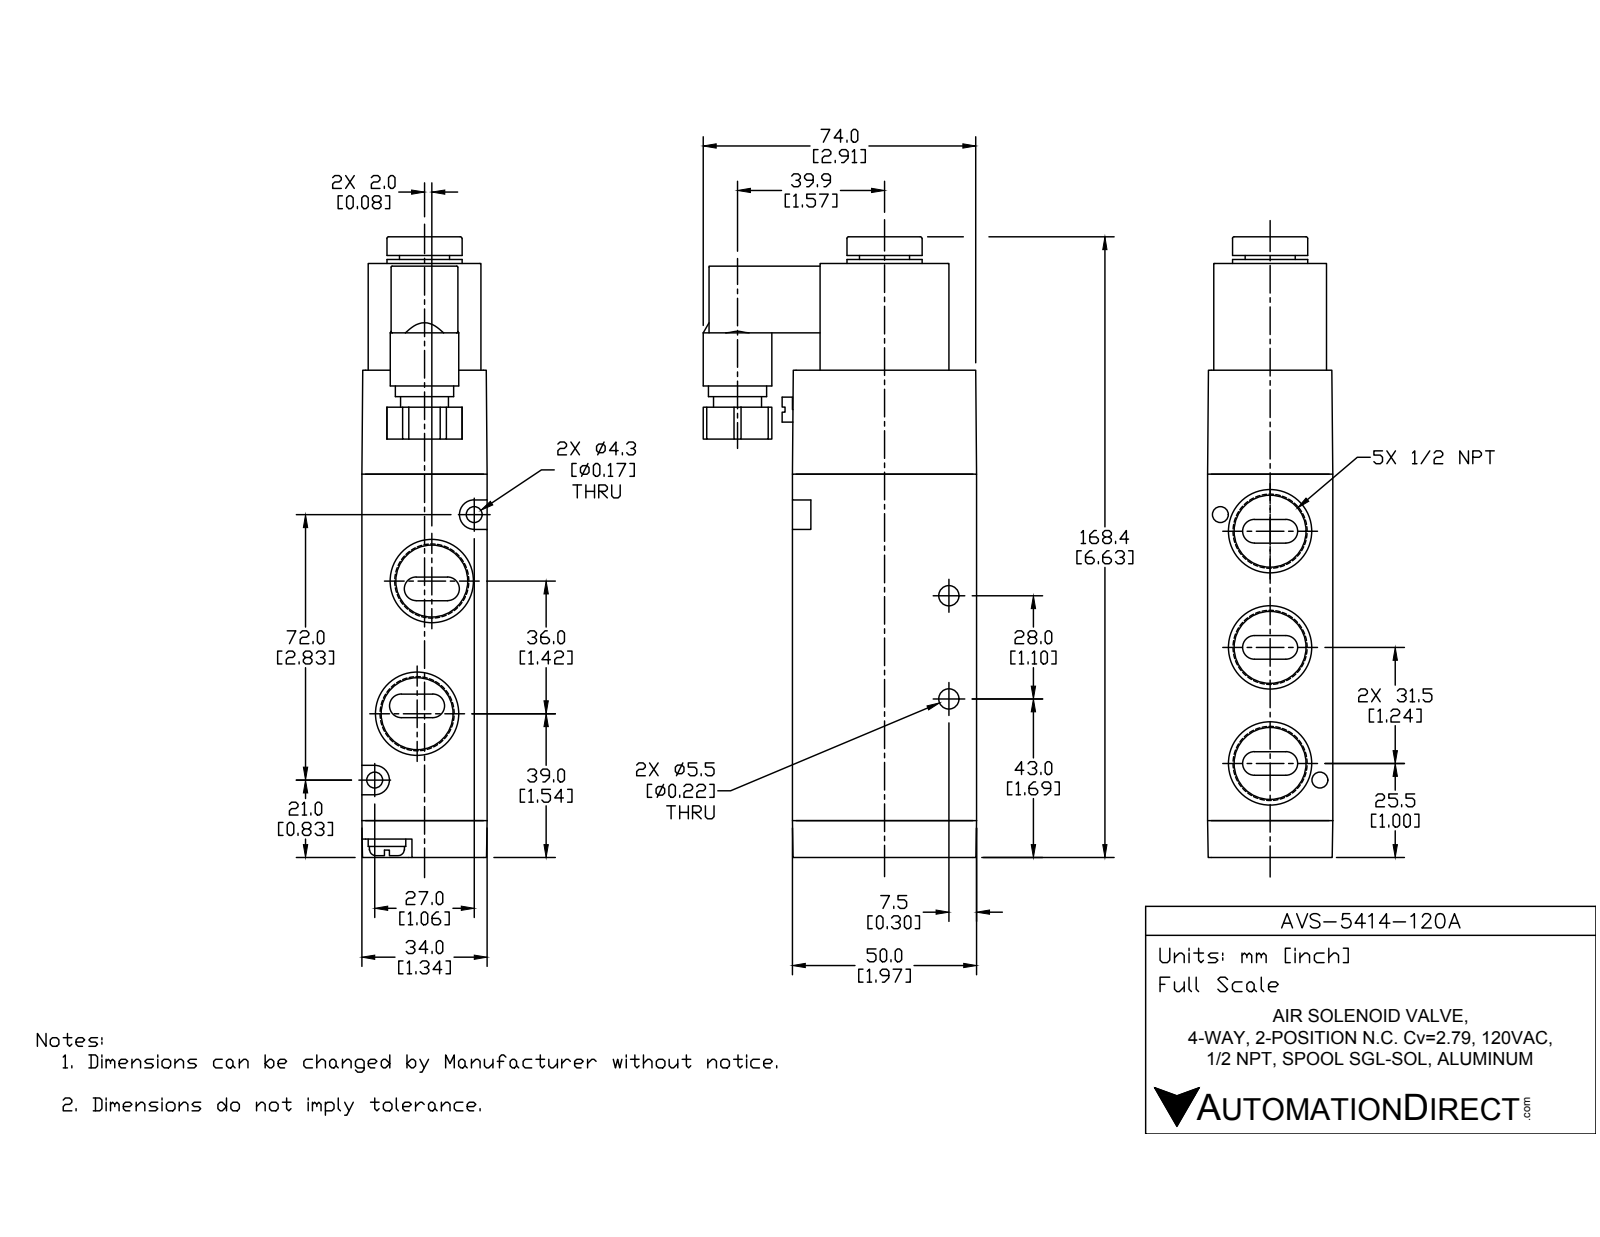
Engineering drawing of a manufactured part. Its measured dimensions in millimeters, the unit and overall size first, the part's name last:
Units: millimetres
Overall size (bounding box): 168.5 × 74.2 × 34
Round holes (diameter × count): ⌀17.86 ×5, ⌀5.5 ×2, ⌀4.3 ×1, ⌀4.4 ×1, ⌀9.3 ×1
Round bosses / shafts (diameter × count): ⌀20.8 ×1, ⌀20.4 ×1, ⌀18.6 ×1, ⌀15.8 ×1, ⌀13.6 ×1, ⌀13 ×1, ⌀6.7 ×1
Partial cylindrical surfaces — rounded edges, fillets, slot ends (radius × count): R1.5 ×12, R3.2 ×10, R1 ×5, R0.5 ×4, R4 ×2
Main face-to-face distances: 34, 94, 50, 10, 104, 28.2, 35.6, 7.95, 26.05, 18.1
Hole centre spacings: 13.65, 14.23, 18.11, 21.36, 31.5, 38.45, 49.54, 56.18
Volume: 243 073 mm³ · Surface area: 48 680 mm²
Bodies: 4 solids, 180 faces (80 planar, 73 cylindrical, 27 other)
Part name (STEP PRODUCT): AVS-5414-120A
STEP written by: SolidWorks 2015 (CONFIG_CONTROL_DESIGN)
